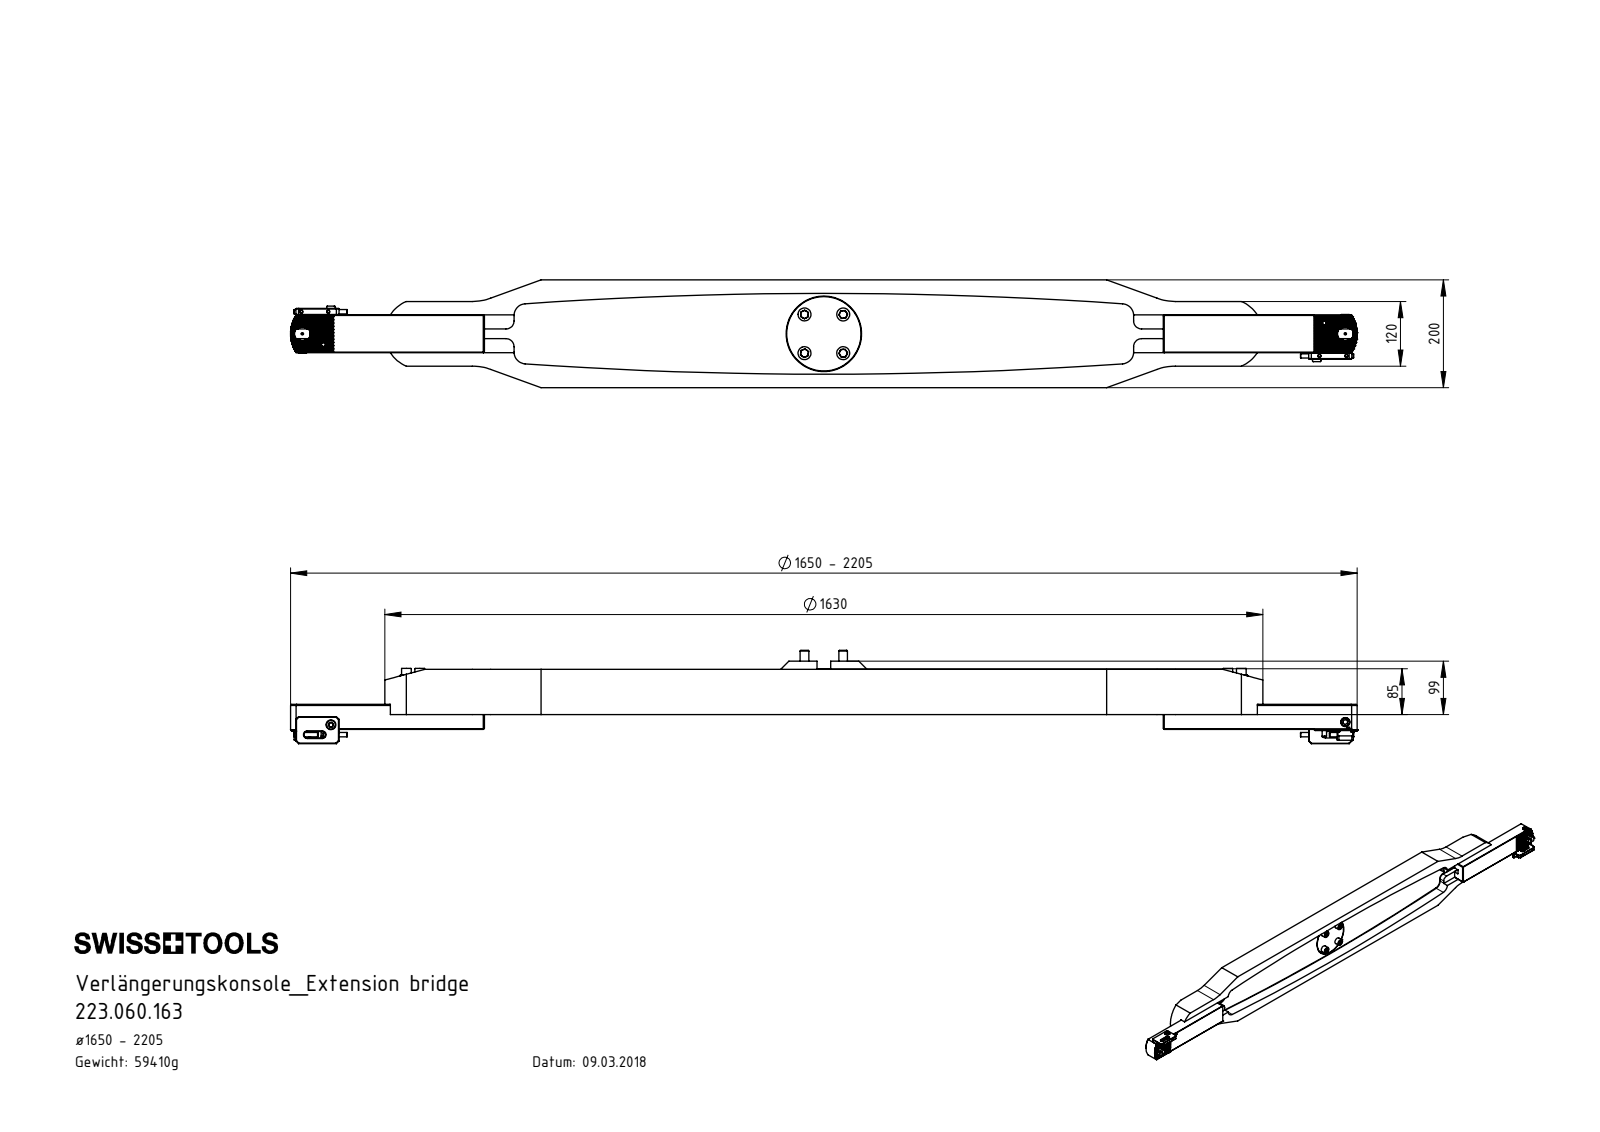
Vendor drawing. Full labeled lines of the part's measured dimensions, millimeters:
Part name (STEP PRODUCT): 223.060.163; VK3-VK1.360.048; ISO 4026 - M8 x 45; ISO 4762 - M10 x 16 (+8 more)
STEP written by: SolidWorks 2017 (CONFIG_CONTROL_DESIGN)
Units: millimetres
Bodies: 46 solids, 2145 faces (916 planar, 736 cylindrical, 493 other)
Overall size (bounding box): 1980 × 200 × 173
Volume: 17 080 000 mm³ · Surface area: 1 497 000 mm²
Round holes (diameter × count): ⌀18 ×42, ⌀10.2 ×40, ⌀13 ×16, ⌀5 ×4, ⌀6 ×4, ⌀6.8 ×4, ⌀12 ×4, ⌀17 ×4, ⌀2 ×2, ⌀8 ×2, ⌀8.5 ×2, ⌀10.5 ×2
Round bosses / shafts (diameter × count): ⌀24 ×12, ⌀16 ×8, ⌀12 ×4, ⌀10 ×2, ⌀8 ×2, ⌀138 ×1
Partial cylindrical surfaces — rounded edges, fillets, slot ends (radius × count): R0.14 ×33, R2 ×22, R22 ×12, R15 ×6, R1.5 ×4, R5.5 ×4, R6 ×4, R8 ×4
Main face-to-face distances: 32, 65, 13, 45, 71, 84, 39, 200, 40, 135
Hole centre spacings: 25, 47.17, 50, 64.03, 40, 75, 85, 1450
